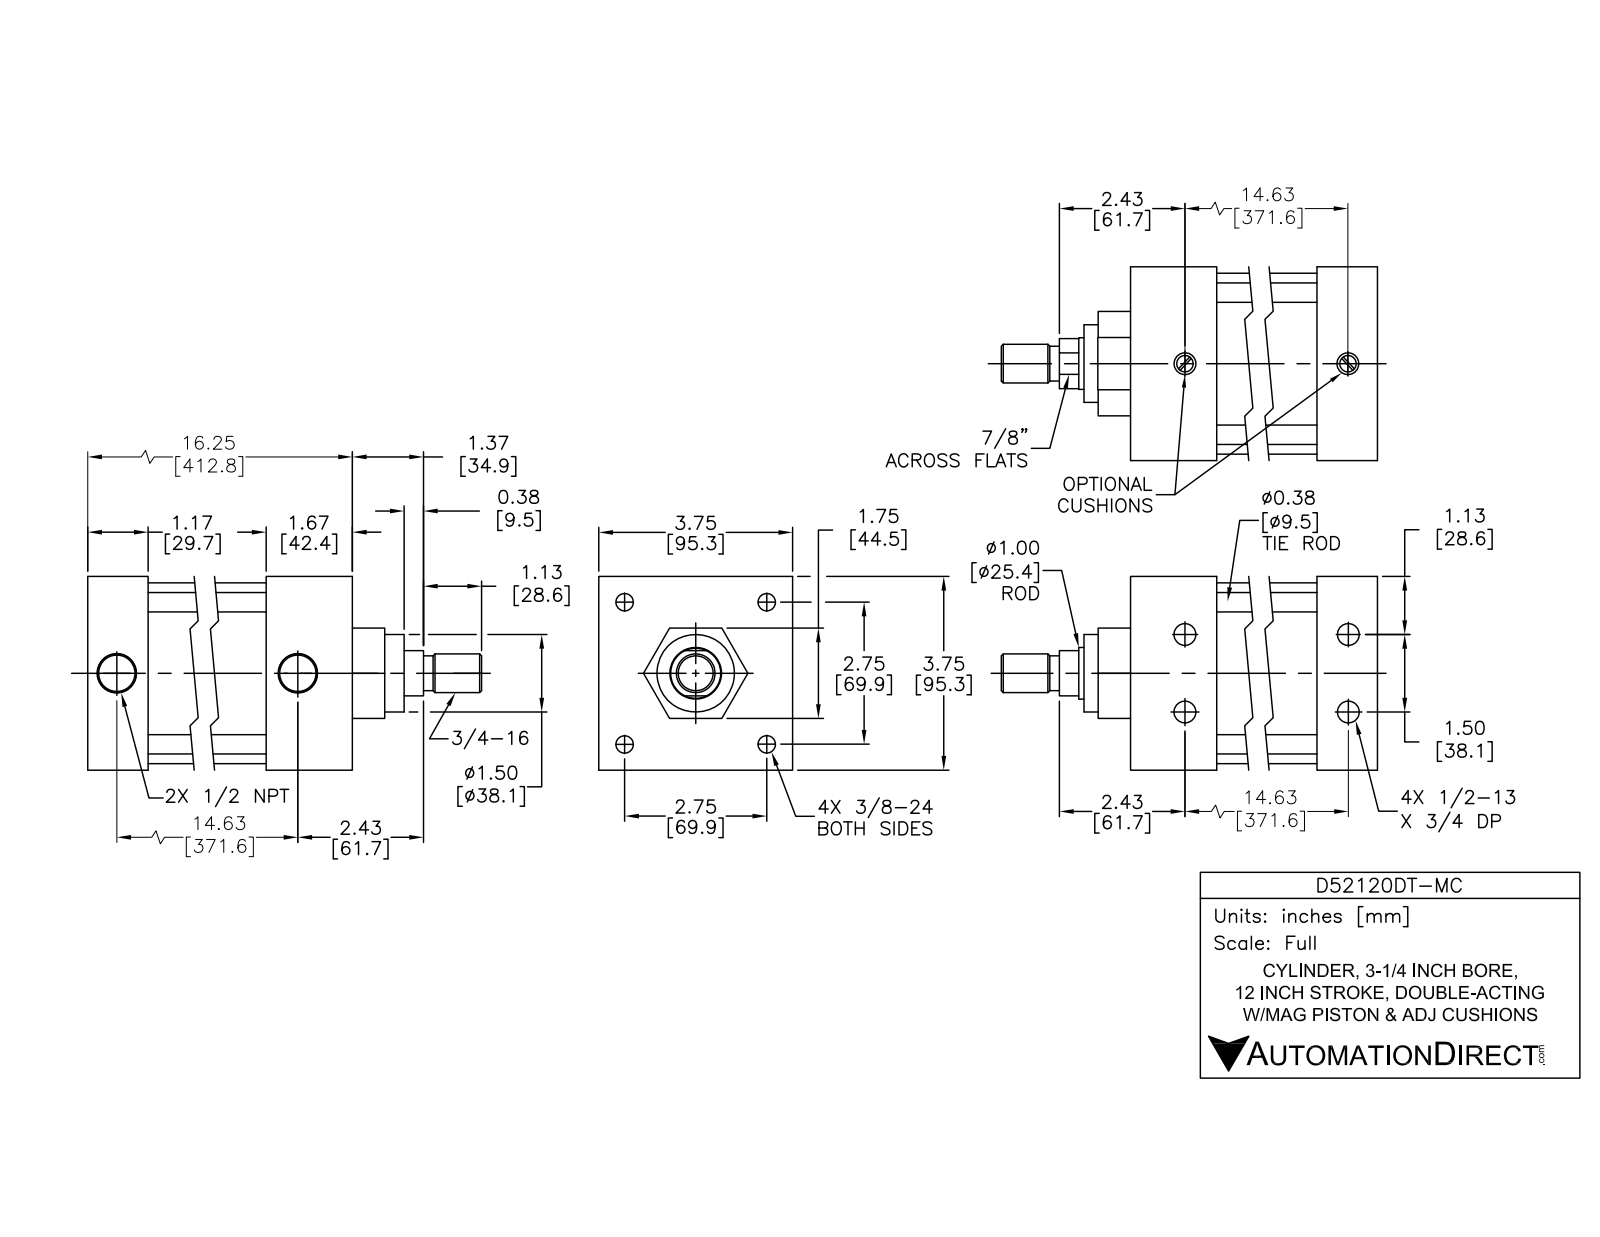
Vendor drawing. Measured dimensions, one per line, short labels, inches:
name: D52120DT-MC; D52120DT-M BODY; D52120DT-M PISTON
written by: SolidWorks 2015 (AUTOMOTIVE_DESIGN)
unit: in
bodies: 12 solids, 303 faces (99 planar, 114 cylindrical, 90 other)
size: 18.745 × 3.75 × 3.75
volume: 83.46 in³; area: 580.4 in²
holes: 4× ⌀0.33, 4× ⌀0.406, 4× ⌀0.417, 4× ⌀0.625, 2× ⌀0.5, 2× ⌀0.766, 1× ⌀1, 1× ⌀1.003, 1× ⌀3.25
bosses: 4× ⌀0.609, 4× ⌀0.375, 4× ⌀0.34, 1× ⌀3.5, 1× ⌀3.247, 1× ⌀1.75, 1× ⌀0.997, 1× ⌀0.97
rounds: 4× R0.375
face distances: 3.75, 16.246, 1.75, 14.997, 1.249, 13.751, 1.246, 2.495, 14.996, 1.245
hole spacings: 0.75, 0.76, 1.5, 1.95, 1.95, 2.758, 2.758, 3.9
